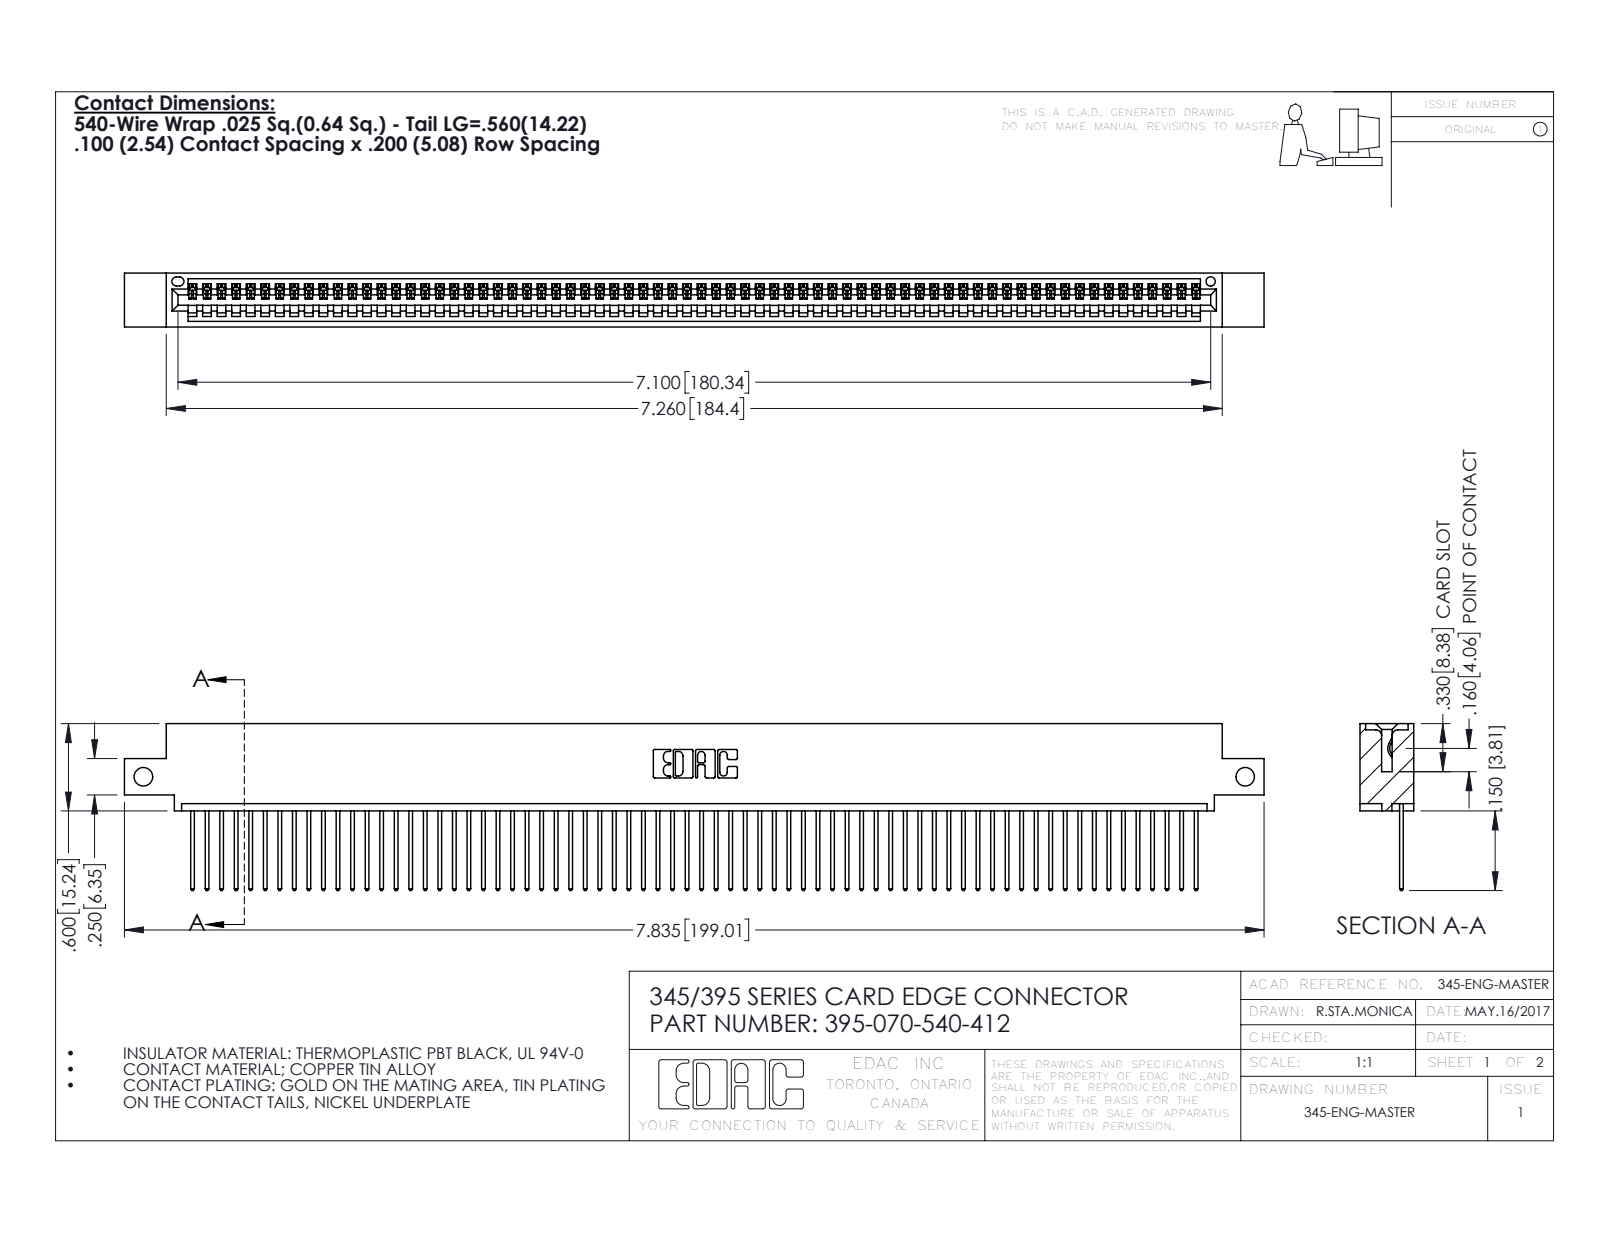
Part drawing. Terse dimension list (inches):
name: 395-070-540-412; 345-292-001_345-293-140; 345 Part_0.110 Offset - Side Mount
written by: SolidWorks 2016 (CONFIG_CONTROL_DESIGN)
unit: in
bodies: 71 solids, 4190 faces (2884 planar, 1306 cylindrical, 0 other)
size: 7.835 × 1.147 × 0.37
volume: 1.163 in³; area: 40.83 in²
holes: 2× ⌀0.128, 1× ⌀0.064
rounds: 140× R0.006, 140× R0.01, 22× R0.01, 6× R0.007, 6× R0.031, 3× R0.026, 2× R0.031, 2× R0.04
face distances: 0.072, 0.298, 0.37, 0.098, 0.272, 0.025, 0.2, 0.225, 0.149, 0.072
hole spacings: 7.575
